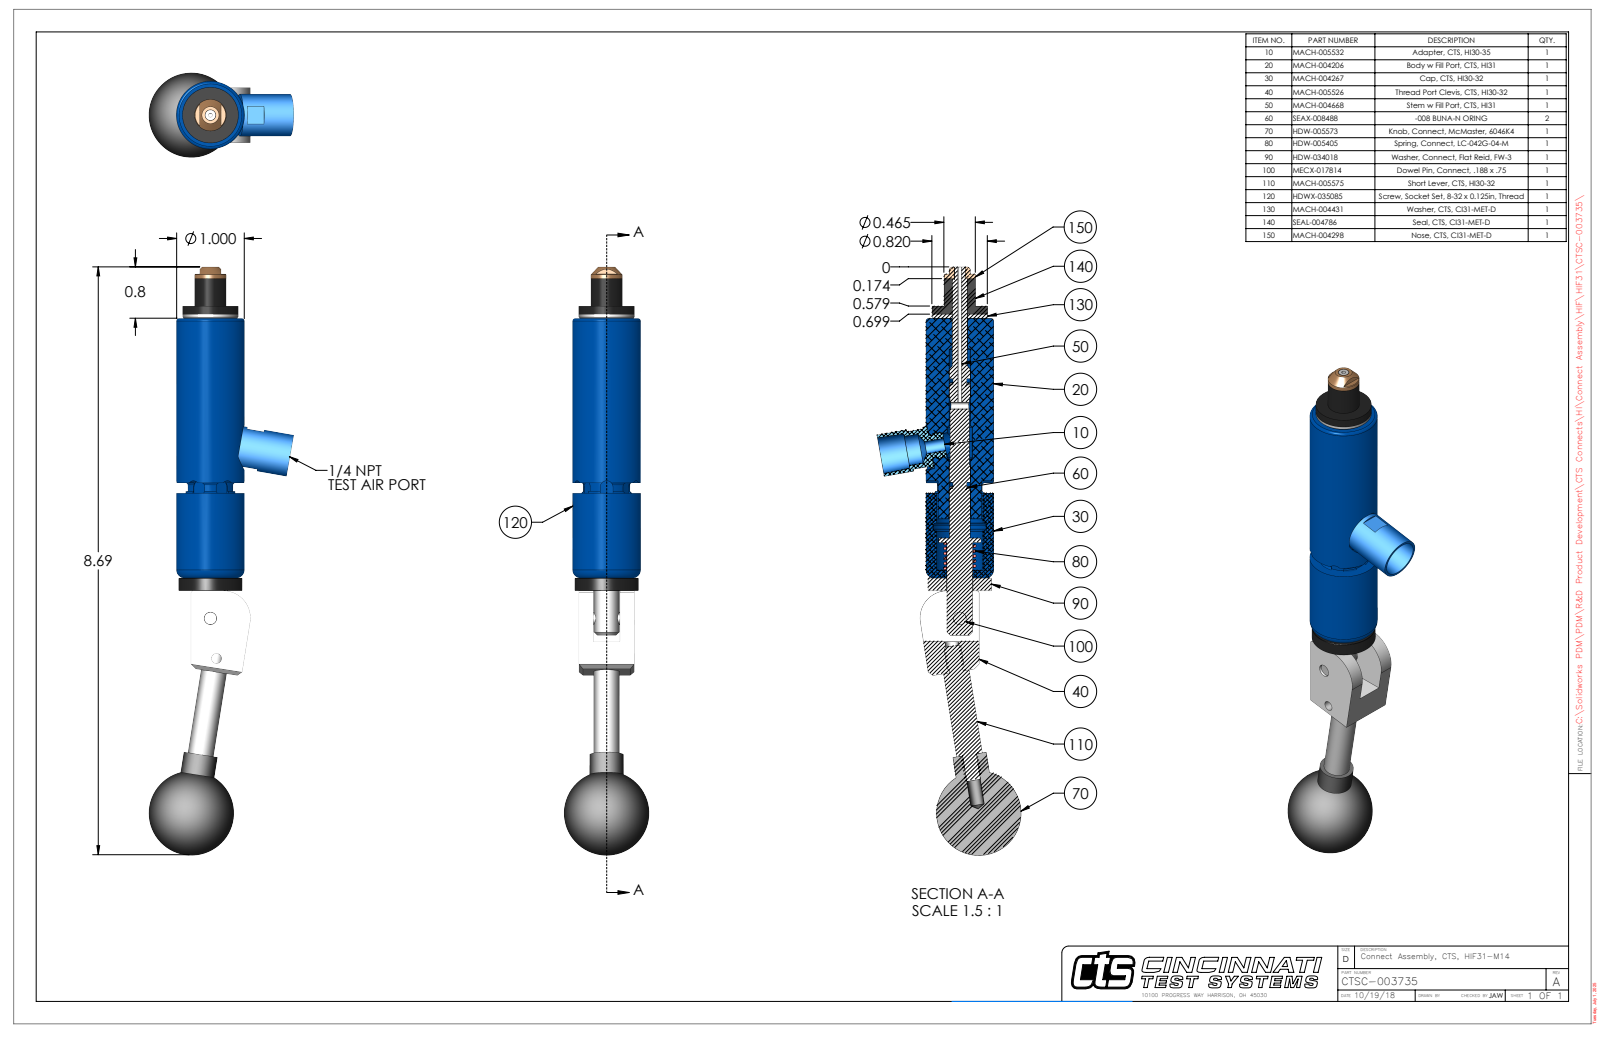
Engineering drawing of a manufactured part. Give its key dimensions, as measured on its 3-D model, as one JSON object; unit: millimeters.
{"part_name": "CTSC-003735", "step_written_by": "SolidWorks 2023 (AUTOMOTIVE_DESIGN)", "units": "millimeters", "bodies": {"solids": 9, "faces": 310, "planar": 121, "cylindrical": 122, "other": 67}, "overall_size": [220.8, 54.1, 31.8], "volume_mm3": 84110, "surface_area_mm2": 25800, "round_holes": [[5.1, 2], [1.6, 1], [2.8, 1], [3.5, 1], [3.8, 1], [4, 1], [4.7, 1], [4.8, 1], [5.5, 1], [5.8, 1], [5.8, 1], [9.8, 1]], "round_bosses_or_shafts": [[25.4, 1], [23.8, 1], [20.8, 1], [15.7, 1], [12.7, 1], [11.8, 1], [11.8, 1], [9.7, 1]], "partial_cylinders_radius": [[2.4, 6], [0.7, 2], [1.6, 1], [8.3, 1], [9.5, 1], [10.2, 1], [11.4, 1]], "face_to_face_distances": [5.3, 15.3, 1.5, 99, 97.4, 20.6, 103.7, 102.2, 4.7, 9.9], "hole_center_spacings": [15.2, 42.1, 57.2]}
